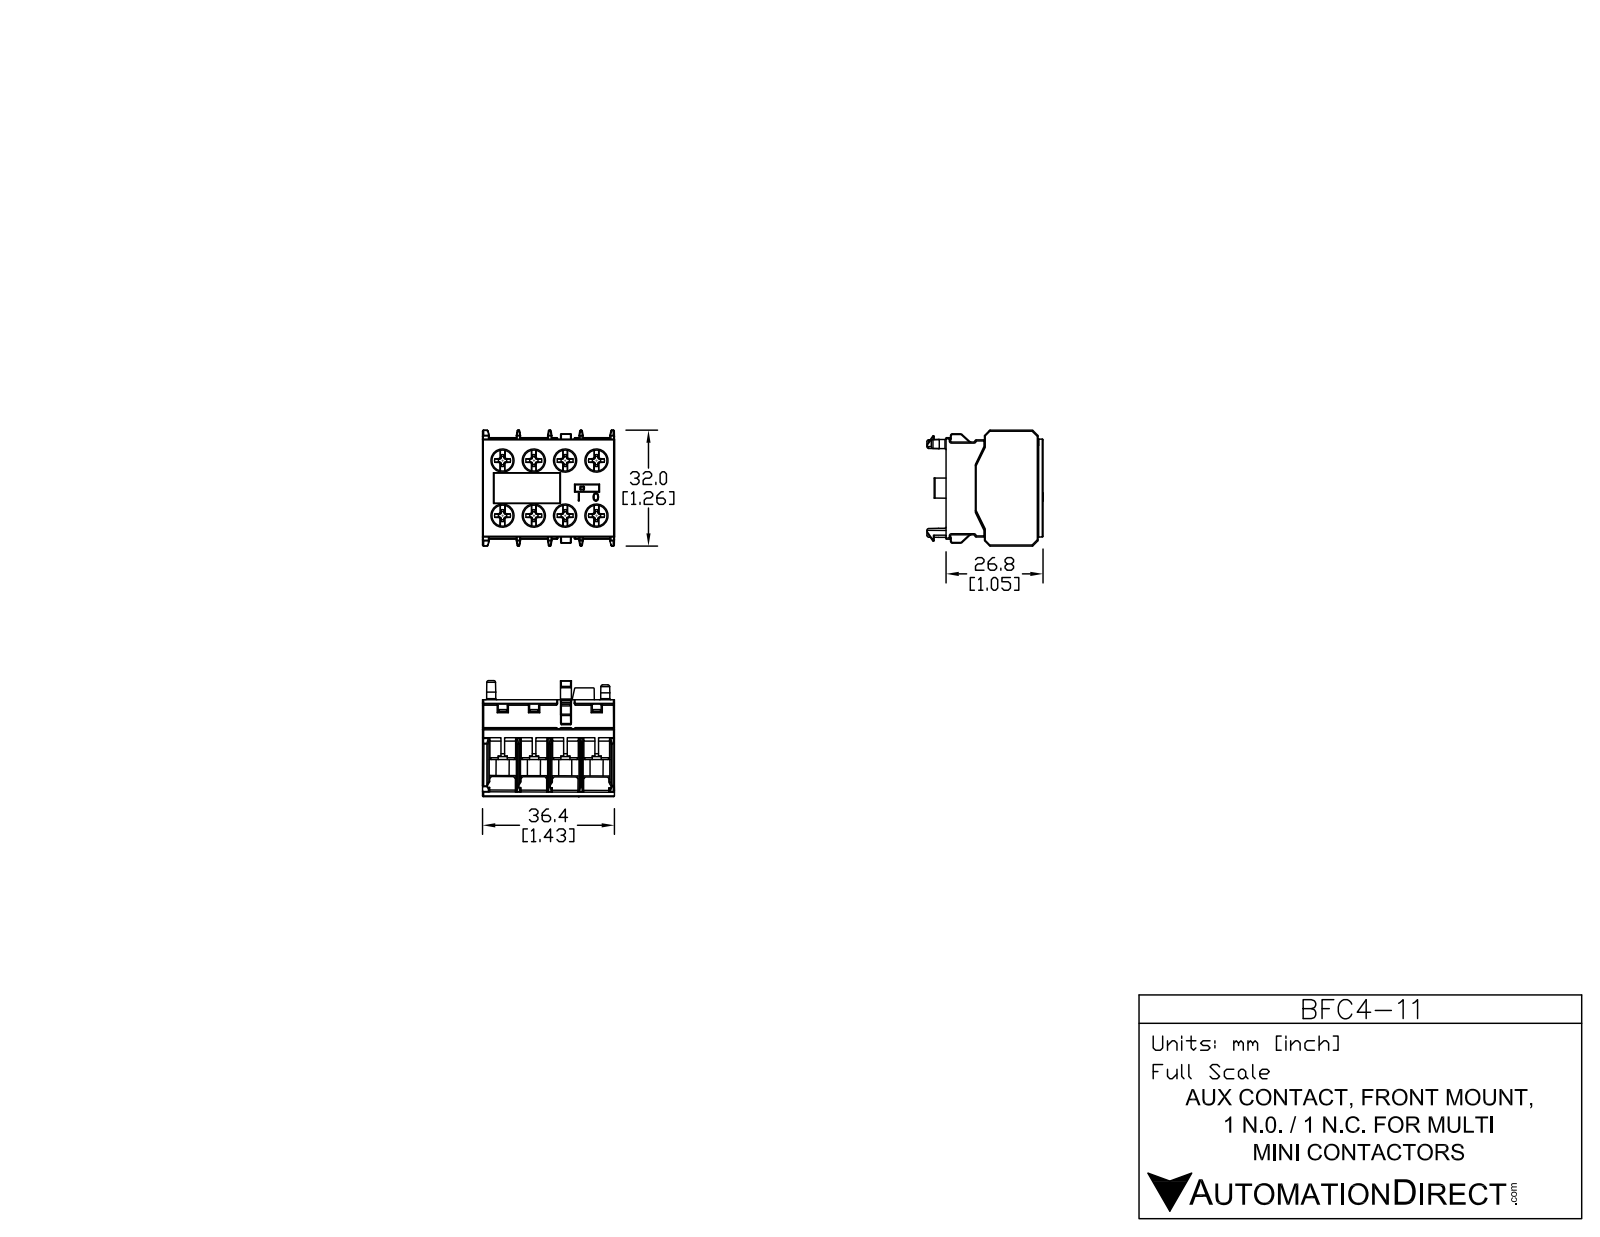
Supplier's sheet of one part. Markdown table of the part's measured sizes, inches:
| quantity | value |
| --- | --- |
| part name | BFC4-11 |
| STEP written by | SolidWorks 2013 (AUTOMOTIVE_DESIGN) |
| units | inches |
| bodies | 20 solids, 761 faces (593 planar, 168 cylindrical, 0 other) |
| overall size | 1.437 × 1.269 × 1.26 |
| volume | 1.002 in³ |
| surface area | 26.95 in² |
| round holes (diameter × count) | 0.236 × 8 |
| round bosses / shafts (diameter × count) | 0.197 × 8, 0.118 × 8, 0.108 × 3 |
| partial cylindrical surfaces (radius × count) | 0.02 × 8, 0.178 × 8, 0.012 × 6, 0.01 × 4, 0.006 × 2, 0.007 × 2, 0.008 × 2 |
| main face-to-face distances | 0.049, 0.679, 0.34, 0.63, 0.339, 1.019, 0.291, 0.728, 0.389, 0.29 |
| hole center spacings | 0.34, 0.591, 0.679, 0.681, 0.9, 0.339, 0.681, 1.019 |
